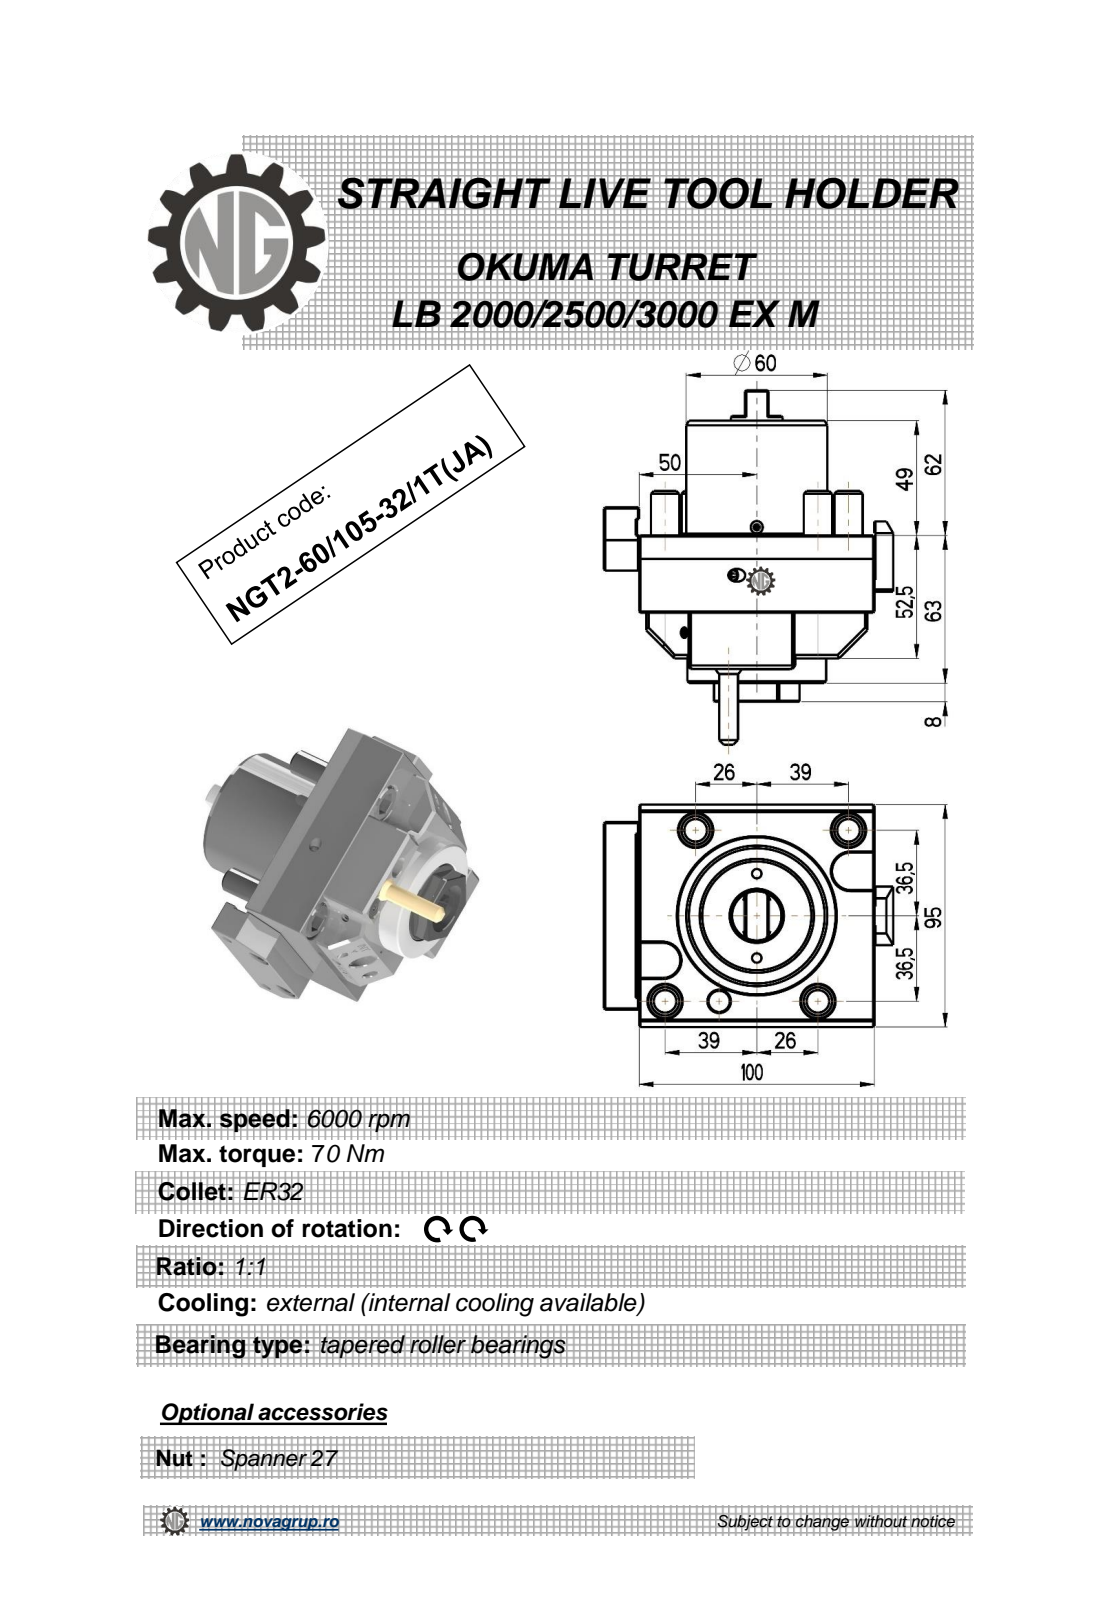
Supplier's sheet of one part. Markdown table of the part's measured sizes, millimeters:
| quantity | value |
| --- | --- |
| part name | NGT2_60_105_32_1T_JA |
| STEP written by | PRO/ENGINEER BY PARAMETRIC TECHNOLOGY CORPORATION, 2010280 (CONFIG_CONTROL_DESIGN) |
| units | millimeters |
| bodies | 1 solid, 323 faces (197 planar, 61 cylindrical, 65 other) |
| overall size | 151.34 × 123 × 95 |
| volume | 657 835 mm³ |
| surface area | 63 235 mm² |
| round holes (diameter × count) | 5 × 3, 3 × 1, 9 × 1, 23 × 1 |
| round bosses / shafts (diameter × count) | 12 × 4, 60 × 1, 59 × 1, 22 × 1, 8 × 1, 6 × 1 |
| partial cylindrical surfaces (radius × count) | 0.31 × 12, 0.26 × 6, 10 × 4, 0.8 × 2, 5.75 × 2, 3.4 × 1, 7.5 × 1, 8 × 1 |
| main face-to-face distances | 63, 15, 33, 0.5, 112, 30, 82, 95, 49, 100 |
| hole center spacings | 4.84, 39.85, 41, 64 |
